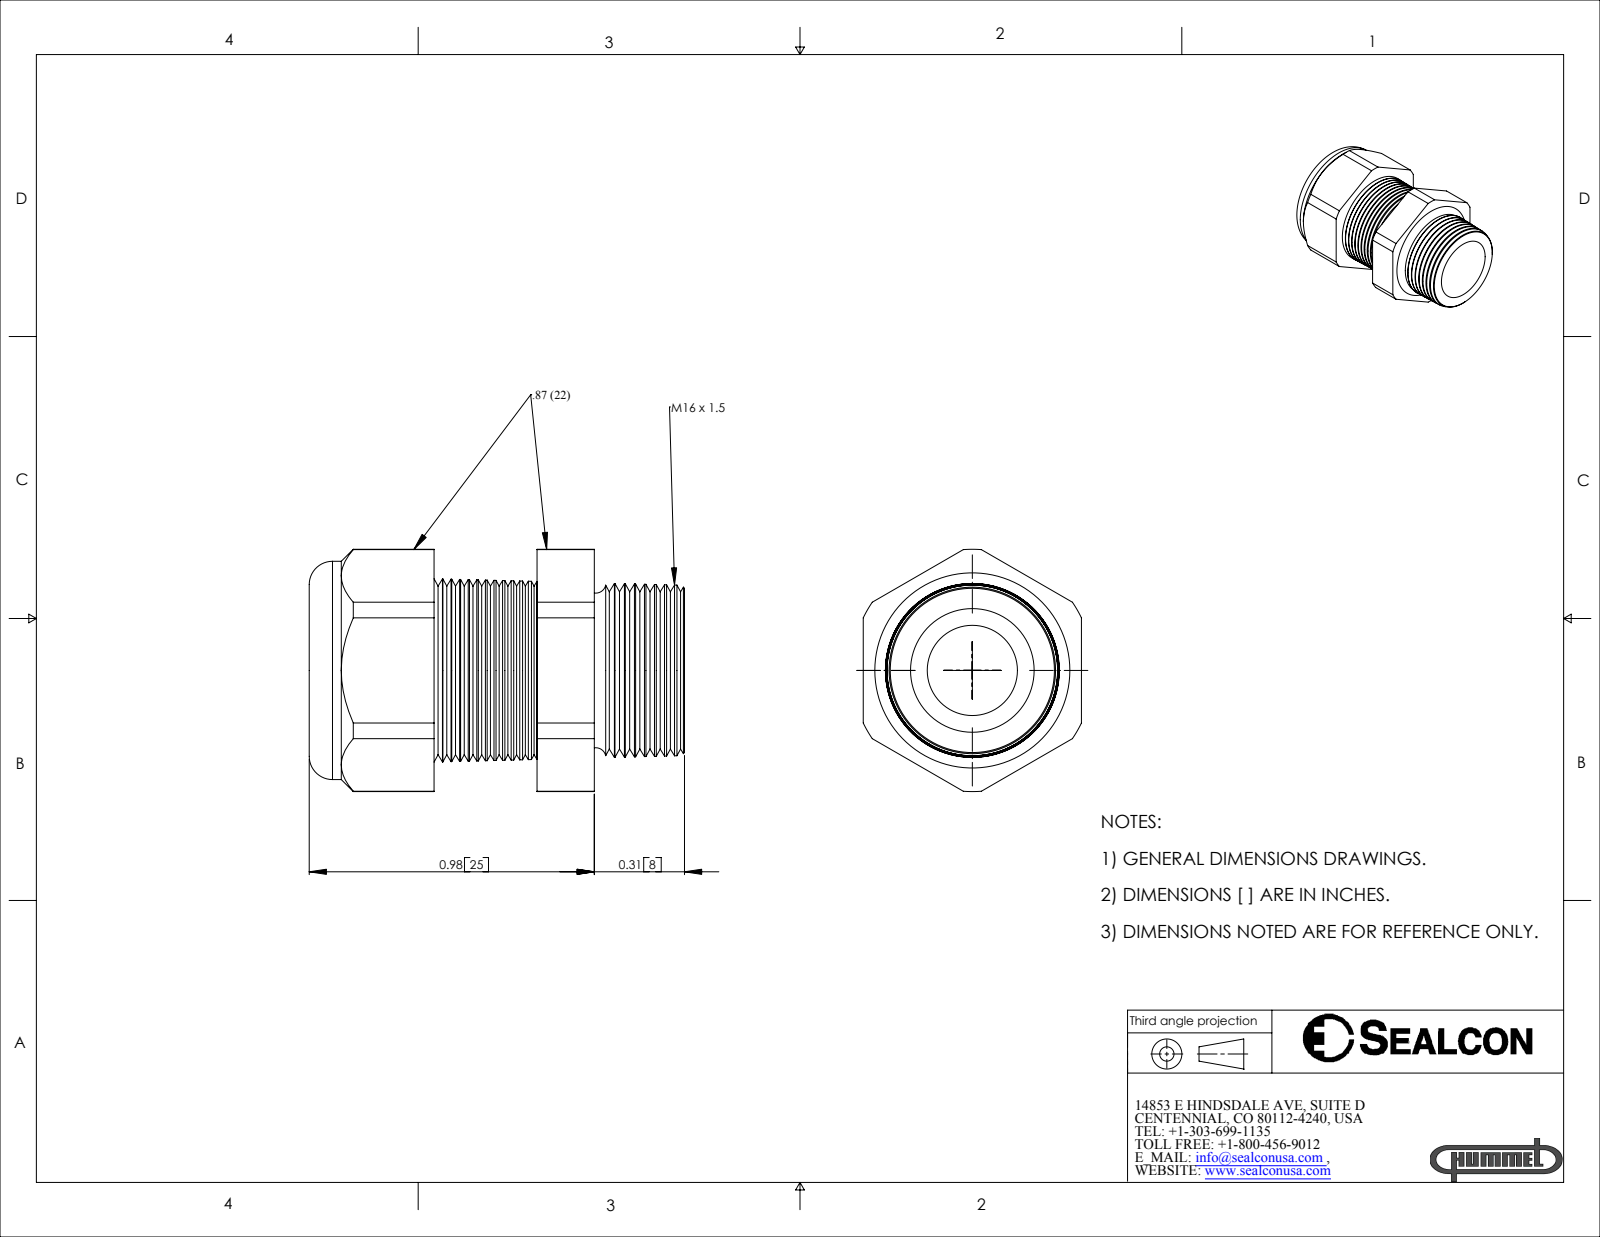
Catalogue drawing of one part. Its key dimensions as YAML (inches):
part_name: "CD17MP-GY"
step_written_by: "SolidWorks 2007 (CONFIG_CONTROL_DESIGN)"
units: inches
bodies: {solids: 2, faces: 179, planar: 21, cylindrical: 20, other: 138}
overall_size: [1.29, 0.833, 0.75]
volume: 0.357
surface_area: 6.6
round_holes:
  - {diameter: 0.29, count: 1}
  - {diameter: 0.31, count: 1}
round_bosses_or_shafts:
  - {diameter: 0.75, count: 1}
partial_cylinders:
  - {radius: 0.416, count: 1}
face_to_face_distances: [0.75, 0.75, 0.783, 0.429, 0.354, 0.98, 0.551, 0.197, 1.29, 0.861]
